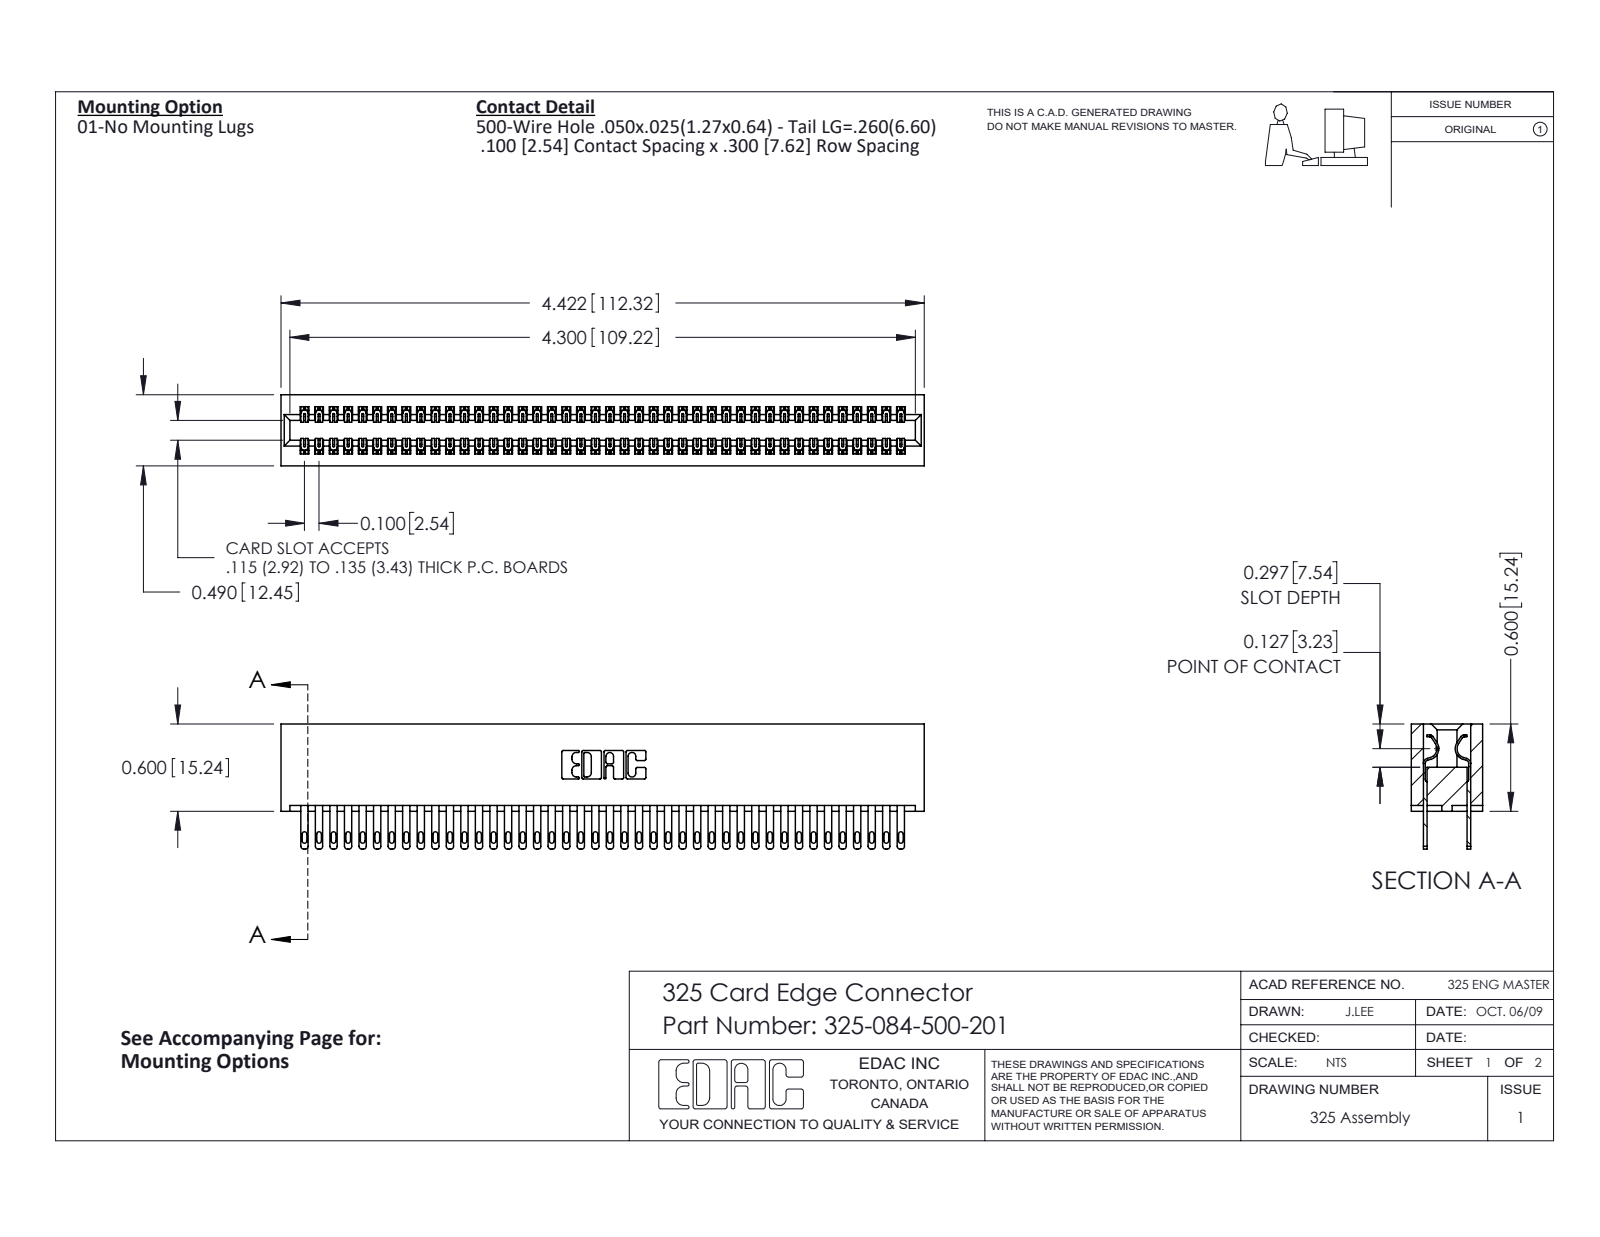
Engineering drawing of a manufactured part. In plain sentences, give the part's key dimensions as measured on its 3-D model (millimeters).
The part is named "325-292-001_325-293-100; 325 Part_Lugless; 325-084-500-201". Its 3-D file was written by "SolidWorks 2016 (CONFIG_CONTROL_DESIGN)". It is 85 solids with 4138 faces: 2586 planar, 1552 cylindrical and 0 other. Overall it measures 112.3 by 21.8 by 12.4 millimeters. Its volume is 15 400 cubic millimeters and its surface area 20 140 square millimeters. Partial cylindrical surfaces (rounded edges, fillets, slot ends): 126 of radius 0.2, 84 of radius 0.4, 84 of radius 0.5, 22 of radius 0.3, 6 of radius 0.2, 6 of radius 0.8, 3 of radius 0.7, 2 of radius 0.4. The main face-to-face distances are 2.1, 10.3, 7.6, 2.7, 9.7, 0.6, 8.3, 12.4, 7, 14.2.
